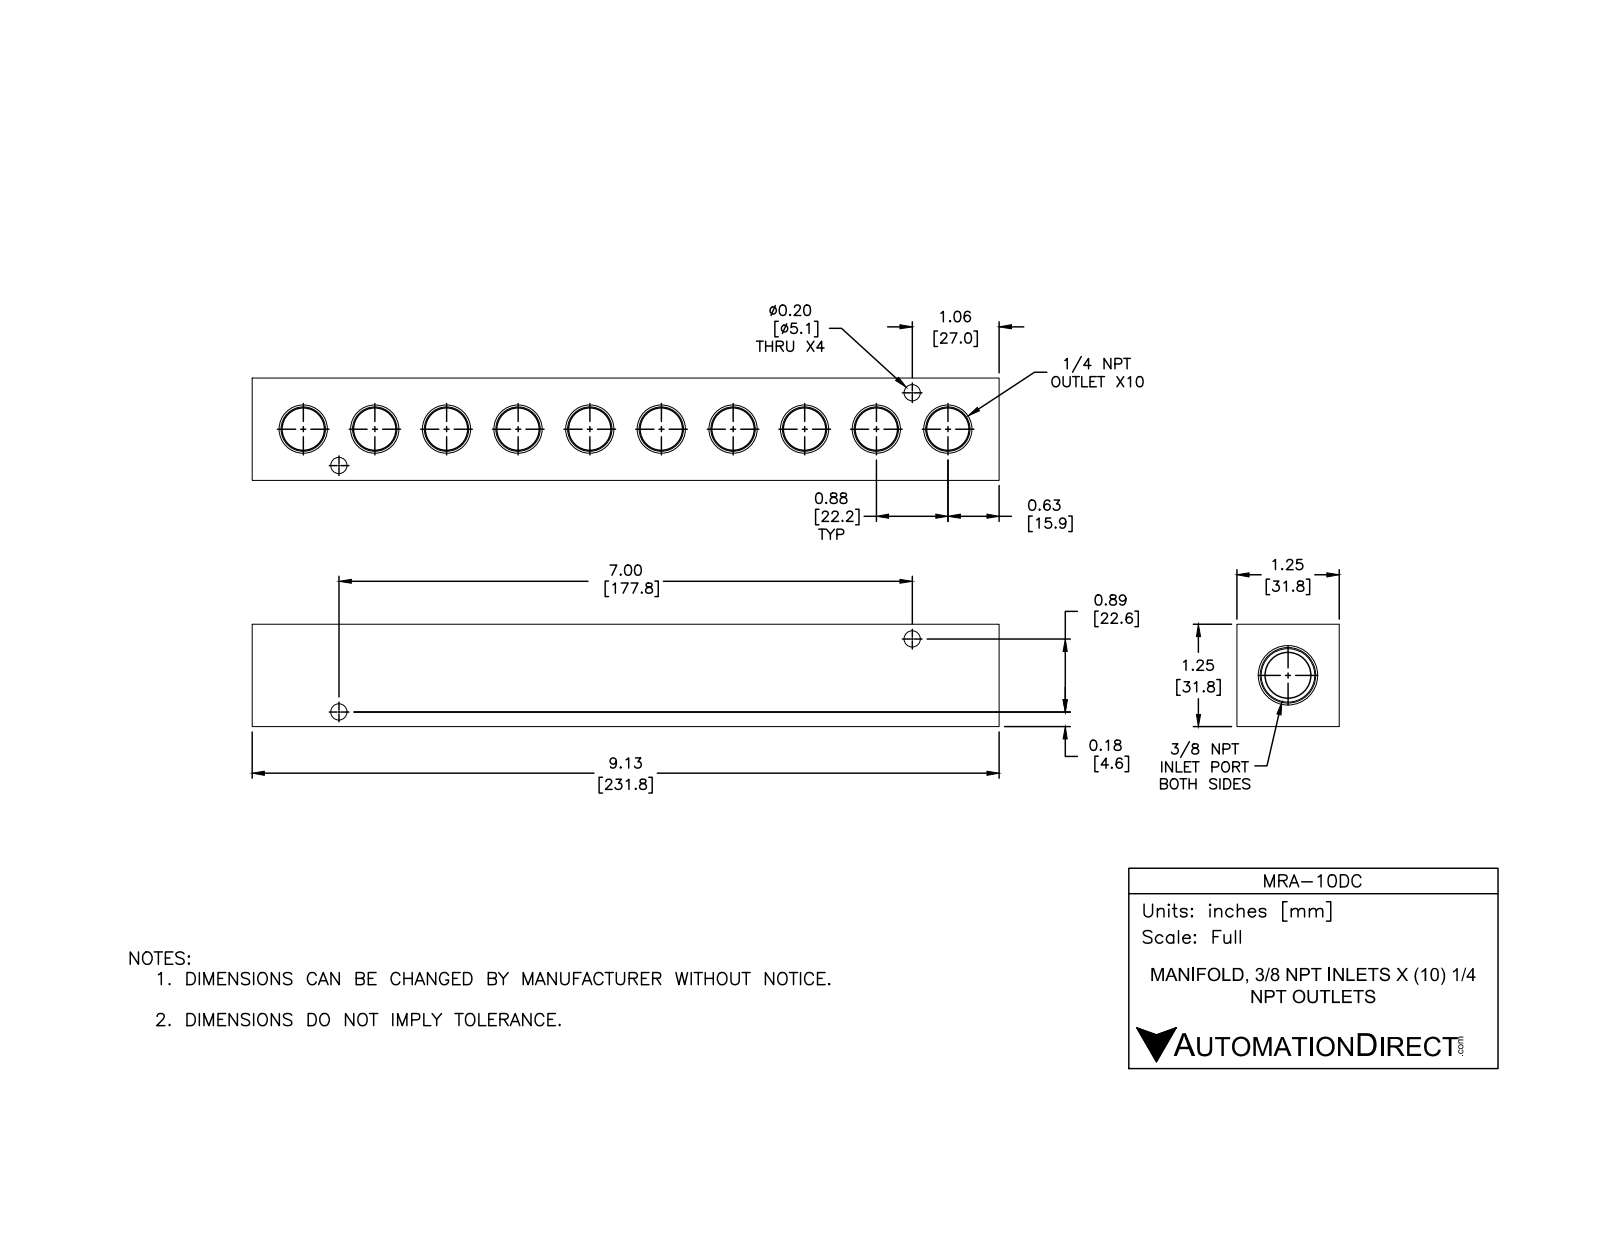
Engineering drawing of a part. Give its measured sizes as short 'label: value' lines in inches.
name: MRA-10DC
written by: SolidWorks 2015 (CONFIG_CONTROL_DESIGN)
unit: in
bodies: 1 solid, 114 faces (28 planar, 38 cylindrical, 48 other)
size: 9.125 × 1.25 × 1.25
volume: 10.94 in³; area: 69.43 in²
holes: 4× ⌀0.2, 1× ⌀0.562
rounds: 10× R0.219
face distances: 1.25, 9.125, 0.86, 0.39, 0.41, 8.715, 8.305
hole spacings: 7.056
